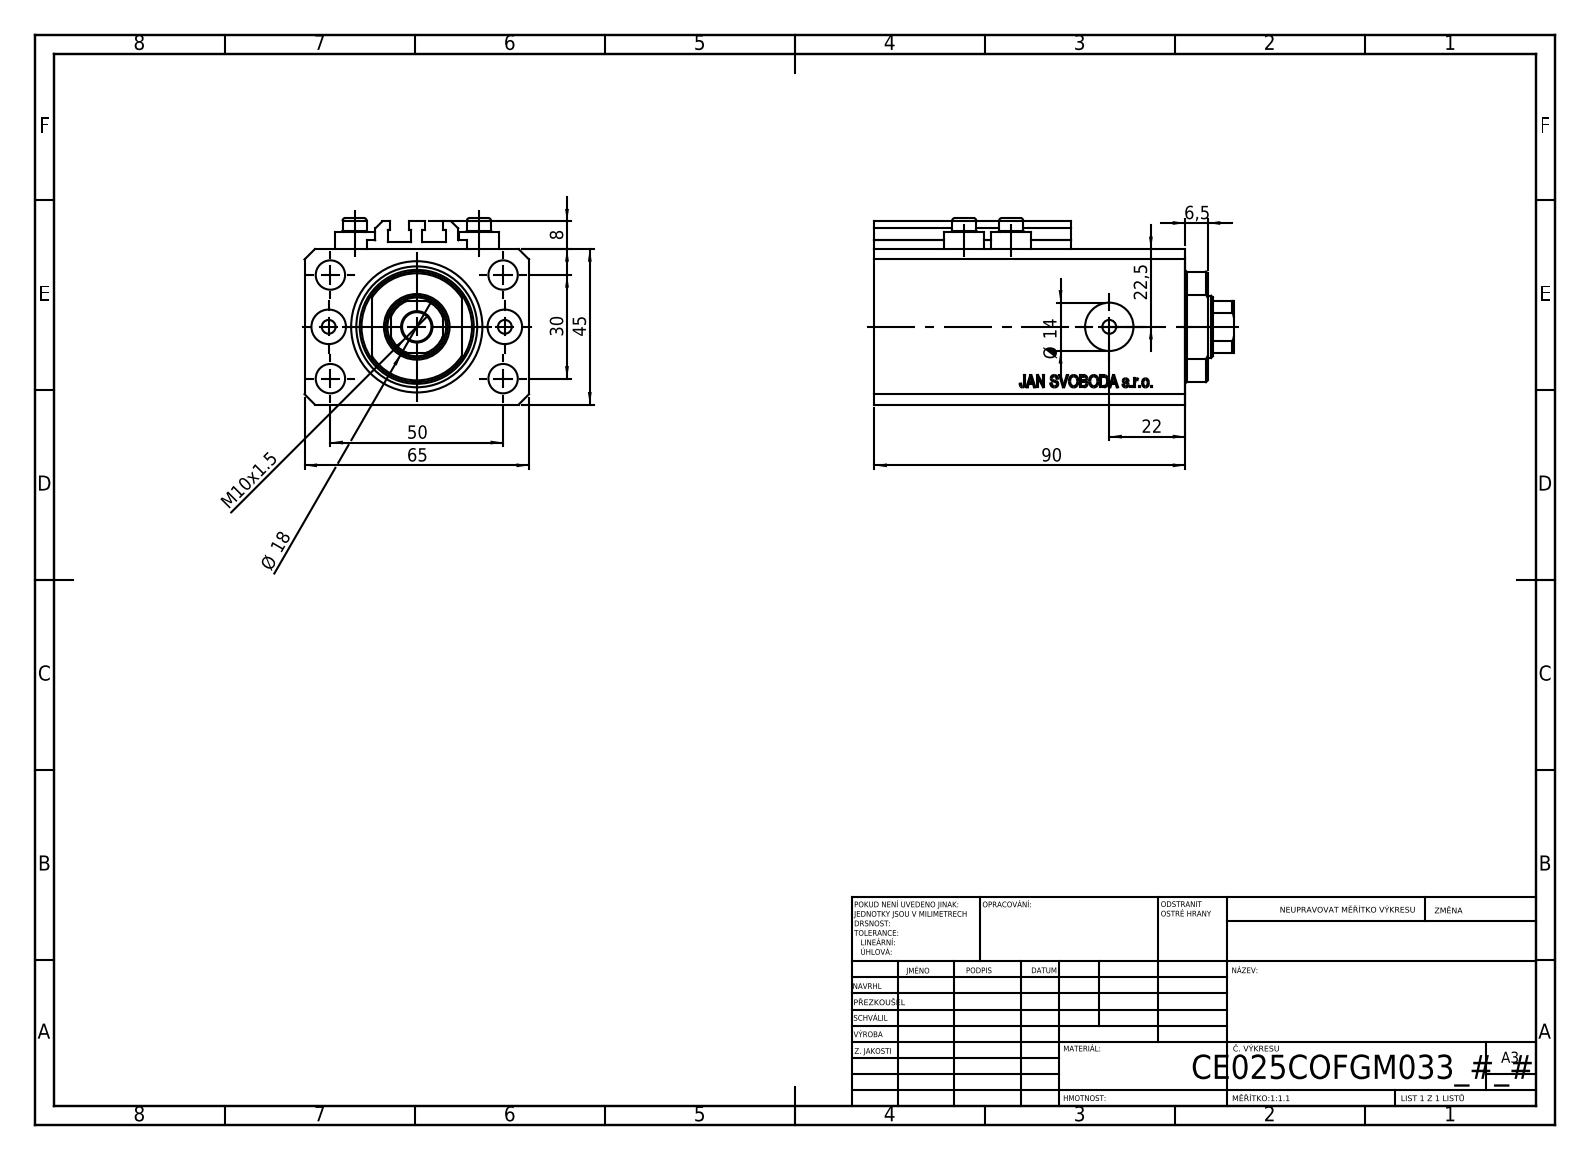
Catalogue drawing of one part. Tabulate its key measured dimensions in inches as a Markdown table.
| quantity | value |
| --- | --- |
| part name | V250CE_VC_C; ALLEN BOLT V250CE; V250CE_C_VCP; V250CE_C_Body |
| STEP written by | SolidWorks 2019 (CONFIG_CONTROL_DESIGN) |
| units | inches |
| bodies | 8 solids, 1034 faces (504 planar, 86 cylindrical, 444 other) |
| overall size | 4.094 × 2.559 × 2.126 |
| volume | 14.97 in³ |
| surface area | 99.96 in² |
| round holes (diameter × count) | 0.157 × 8, 0.335 × 5, 0.394 × 2, 0.551 × 2, 0.709 × 1, 0.984 × 1, 1.496 × 1 |
| round bosses / shafts (diameter × count) | 0.457 × 4, 0.276 × 4 |
| partial cylindrical surfaces (radius × count) | 0.008 × 10, 0.335 × 1, 0.63 × 1 |
| main face-to-face distances | 1.772, 2.559, 0.551, 2.992, 3.543, 1.85, 0.272, 2.72, 3.272, 0.118 |
| hole center spacings | 0.591, 1.148, 2.074, 0.535, 1.004, 1.181, 1.417, 1.515 |
